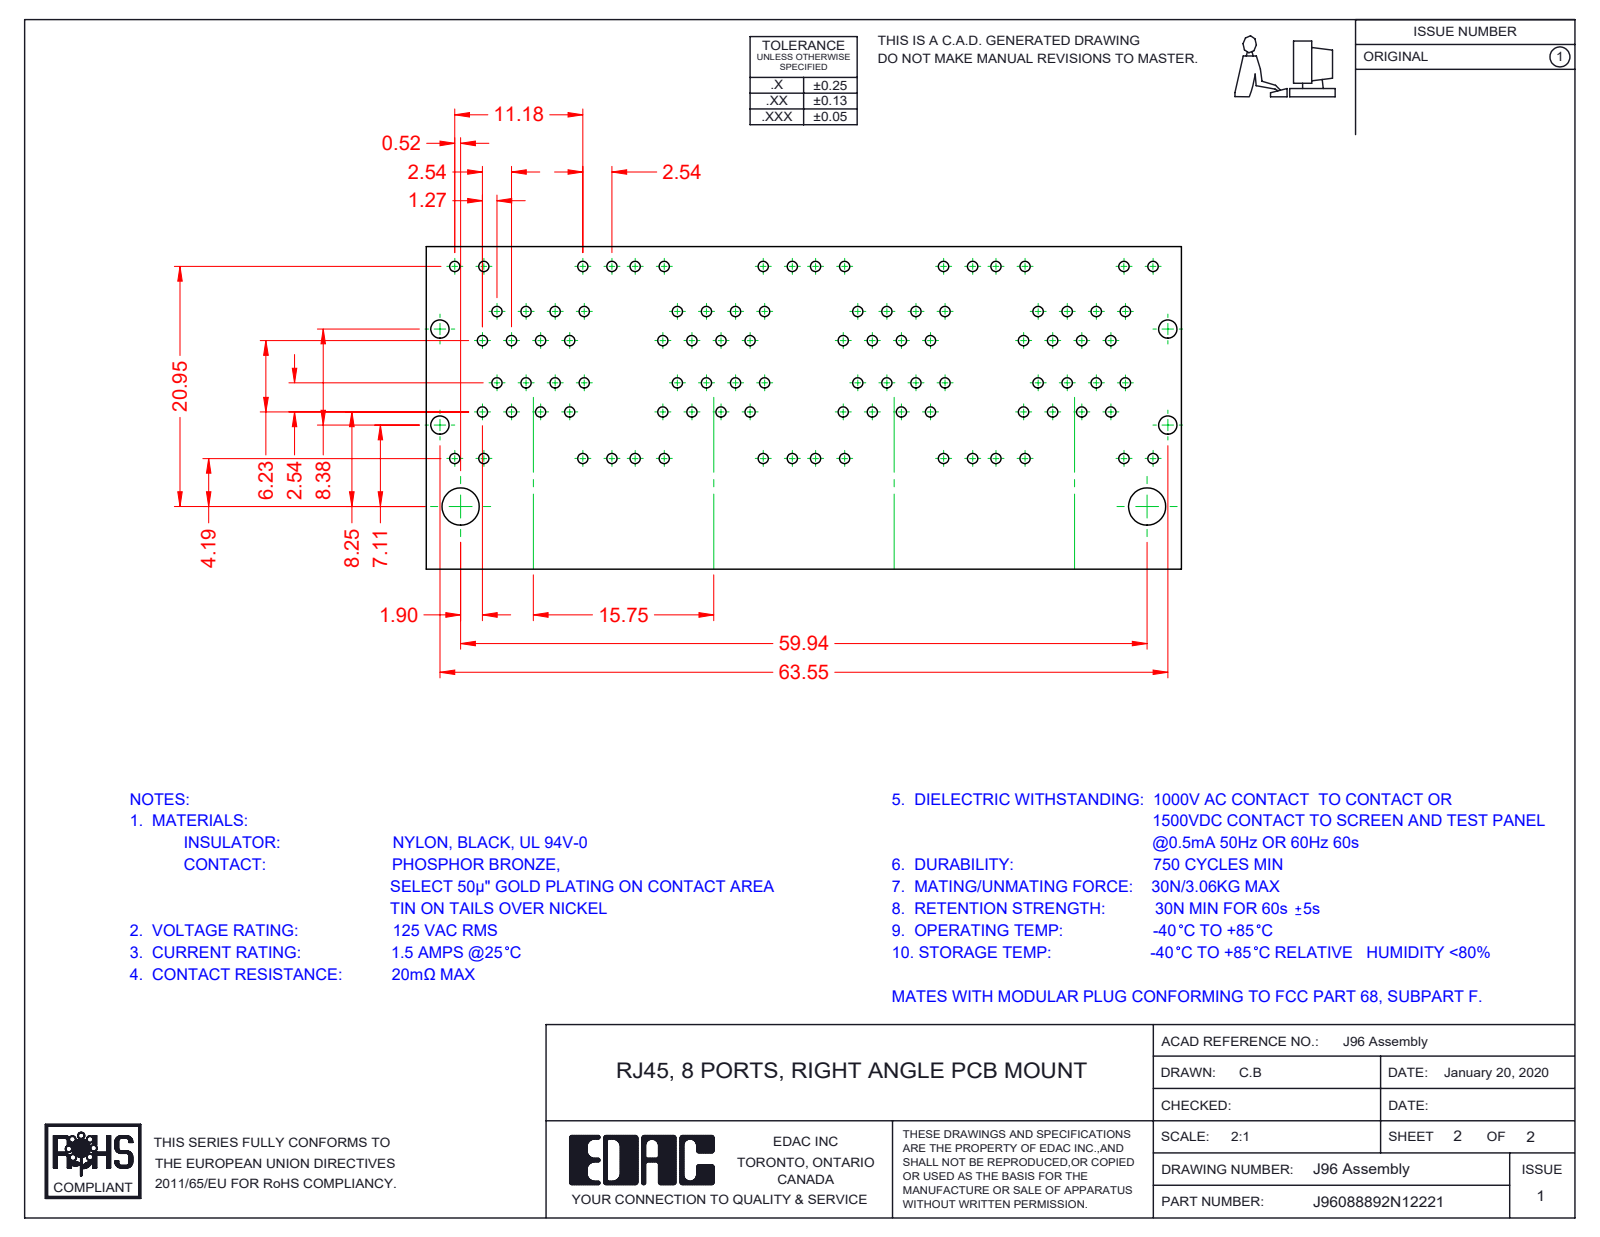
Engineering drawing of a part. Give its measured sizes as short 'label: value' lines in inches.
name: 96 Back Plate_8 Ports; 96 Grounding_8 Ports; 96 Contacts Lower; 96 LED RH Upper_2-Red (+8 more)
written by: SolidWorks 2016 (CONFIG_CONTROL_DESIGN)
unit: in
bodies: 96 solids, 7804 faces (6105 planar, 1388 cylindrical, 311 other)
size: 2.652 × 1.235 × 1.129
volume: 1.474 in³; area: 98.57 in²
holes: 3× ⌀0.067
bosses: 3× ⌀0.066
rounds: 124× R0.01, 73× R0.014, 72× R0.039, 49× R0.02, 32× R0.036, 27× R0.008, 14× R0.011, 11× R0.028
face distances: 0.62, 0.014, 0.392, 0.046, 0.063, 0.021, 0.393, 0.401, 0.499, 0.133
hole spacings: 0.62, 1.24
